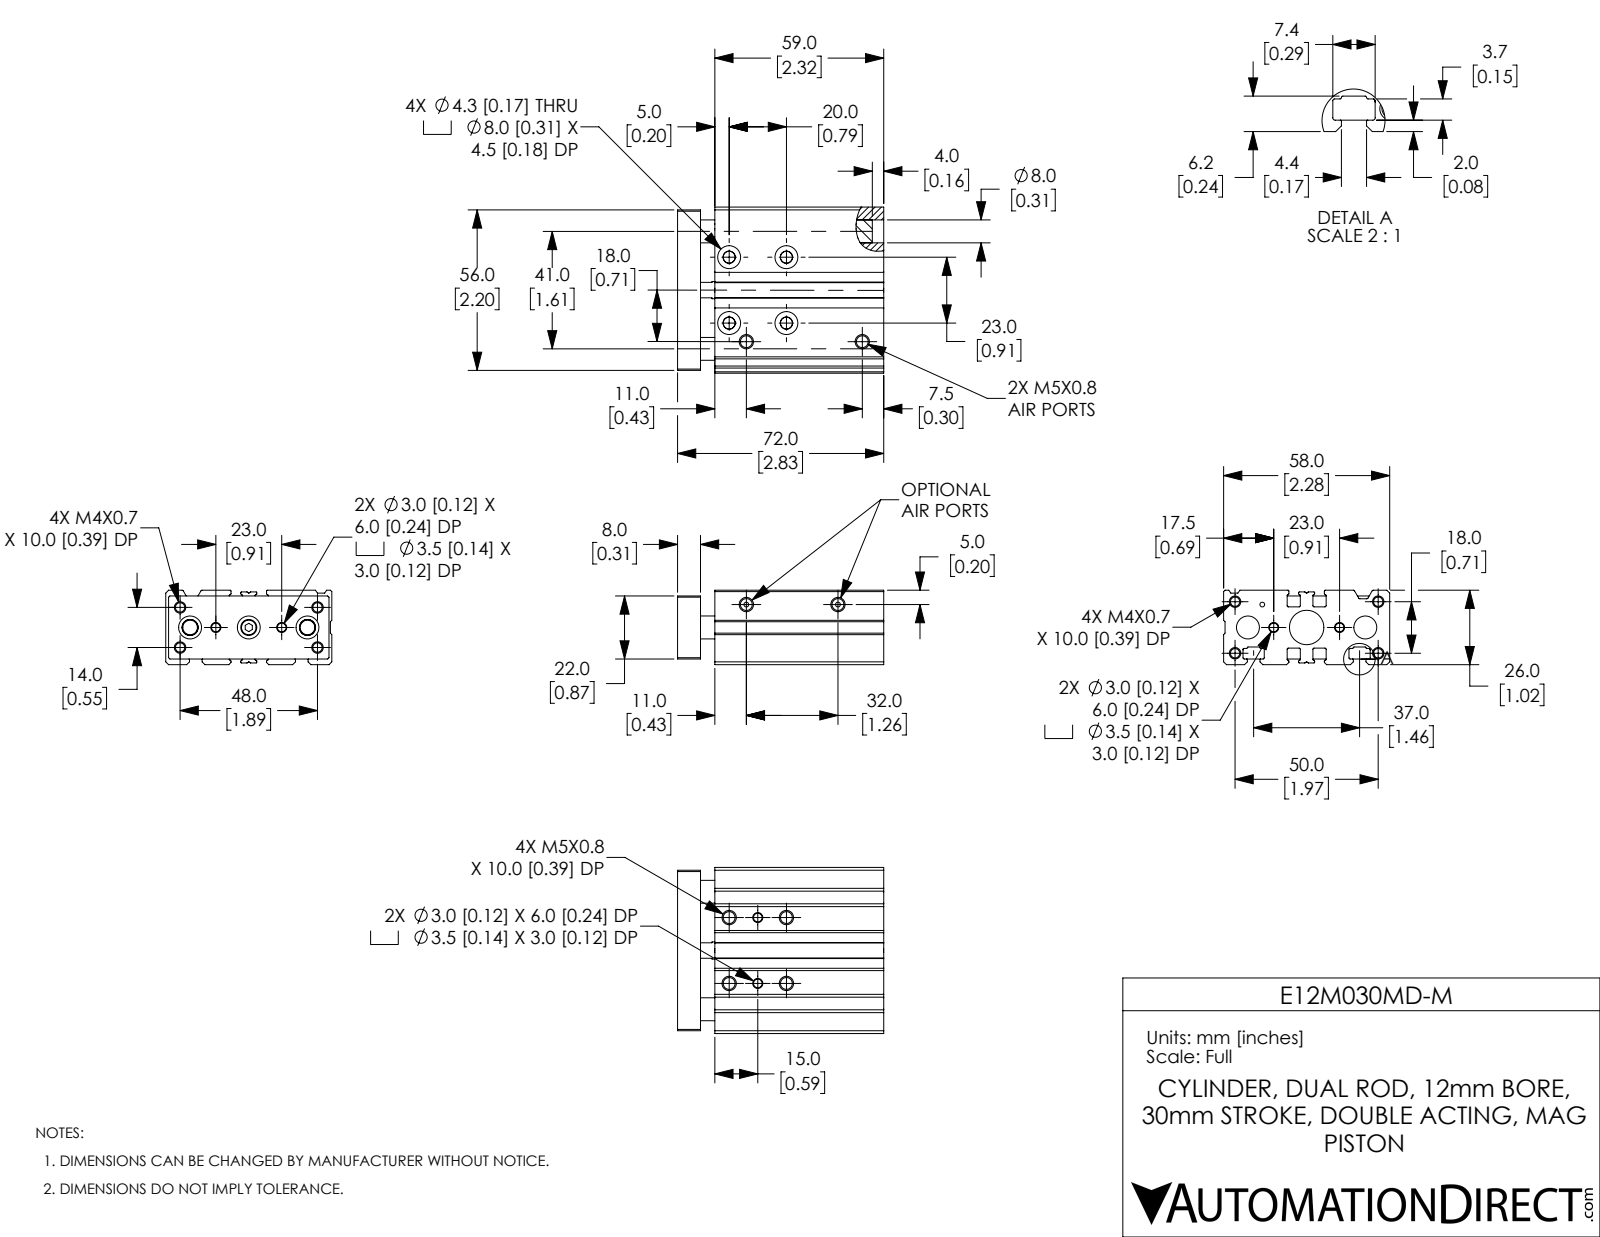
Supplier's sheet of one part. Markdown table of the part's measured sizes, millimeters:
| quantity | value |
| --- | --- |
| part name | E12M030MD-M_ENDPLATE; E12M030MD-D_BODY; E12M030MD-M |
| STEP written by | SolidWorks 2019 (CONFIG_CONTROL_DESIGN) |
| units | millimeters |
| bodies | 5 solids, 413 faces (137 planar, 188 cylindrical, 88 other) |
| overall size | 72 × 58 × 26 |
| volume | 80 298 mm³ |
| surface area | 34 877 mm² |
| round holes (diameter × count) | 3.24 × 8, 4.13 × 8, 8 × 7, 3 × 4, 3.5 × 4, 4.3 × 4, 1.67 × 3, 4 × 3, 5.59 × 2, 8 × 1, 12 × 1, 12 × 1 |
| round bosses / shafts (diameter × count) | 6 × 1, 5.59 × 1 |
| partial cylindrical surfaces (radius × count) | 0.4 × 20, 0.2 × 18, 0.25 × 8, 0.3 × 6, 0.5 × 4 |
| main face-to-face distances | 26, 8, 2, 5.8, 13, 64, 58, 24, 5, 59 |
| hole center spacings | 2.24, 7.83, 10, 10.06, 14.33, 16.03, 16.22, 23 |
